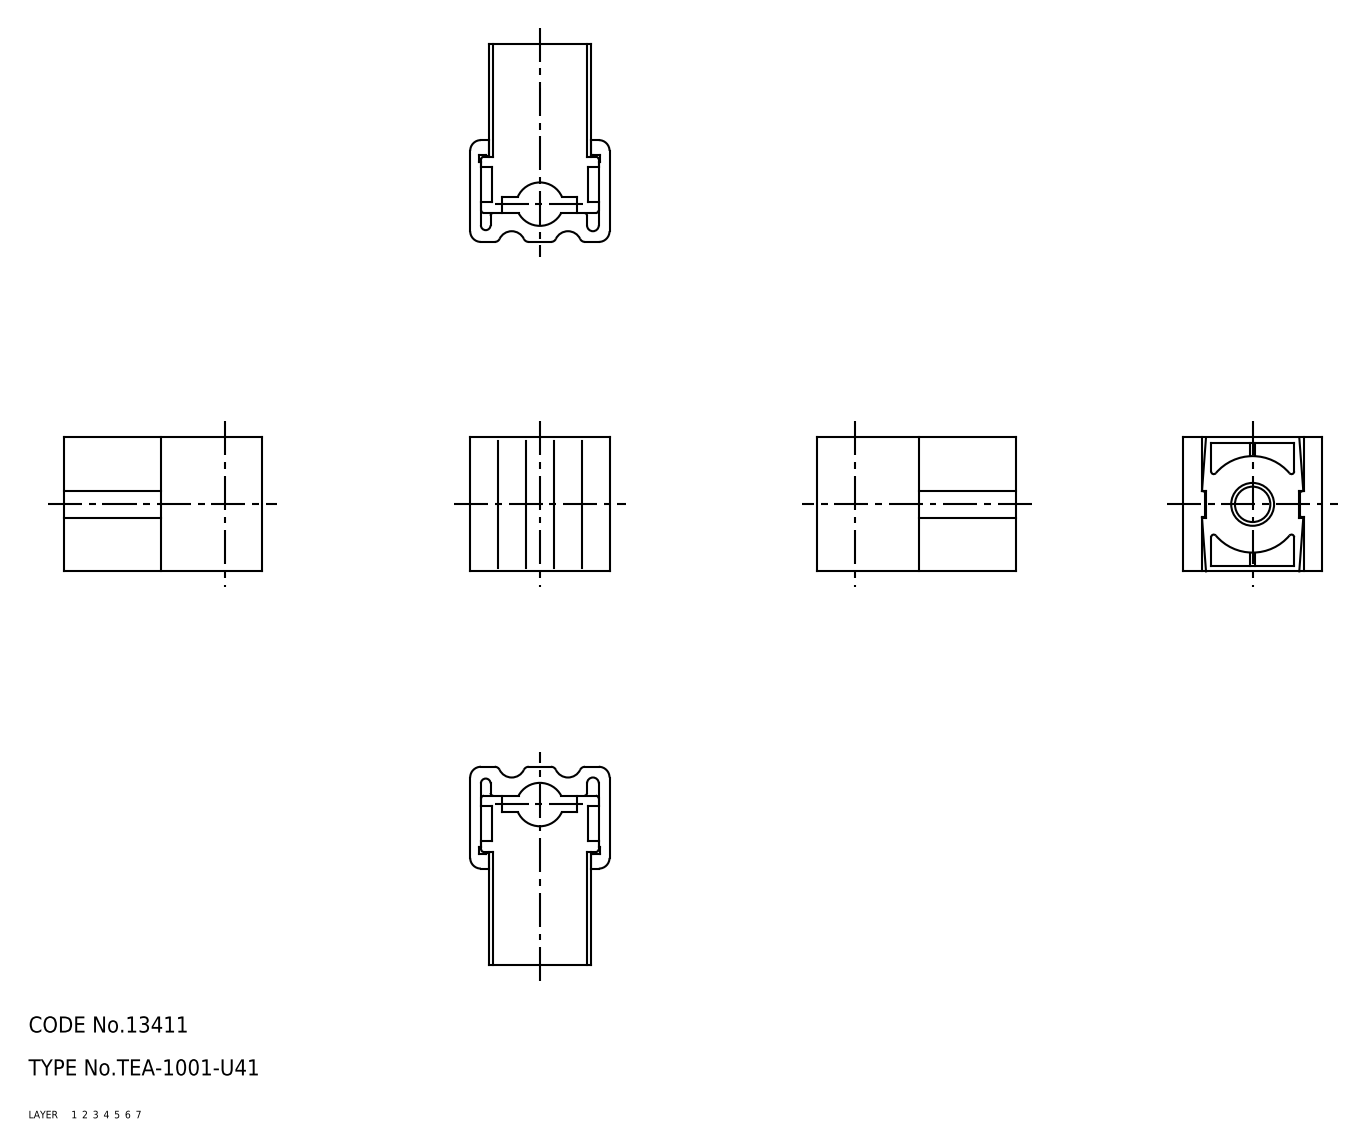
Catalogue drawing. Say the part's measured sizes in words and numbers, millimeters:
The part is named "guide_2; guide_1; TEA_1001_U41_7422_36". Its 3-D file was written by "CADfix (AUTOMOTIVE_DESIGN)". It is 2 solids with 125 faces: 0 planar, 0 cylindrical and 125 other. Overall it measures 37 by 26 by 25 millimeters. Its volume is 10 878 cubic millimeters and its surface area 10 732 square millimeters.
